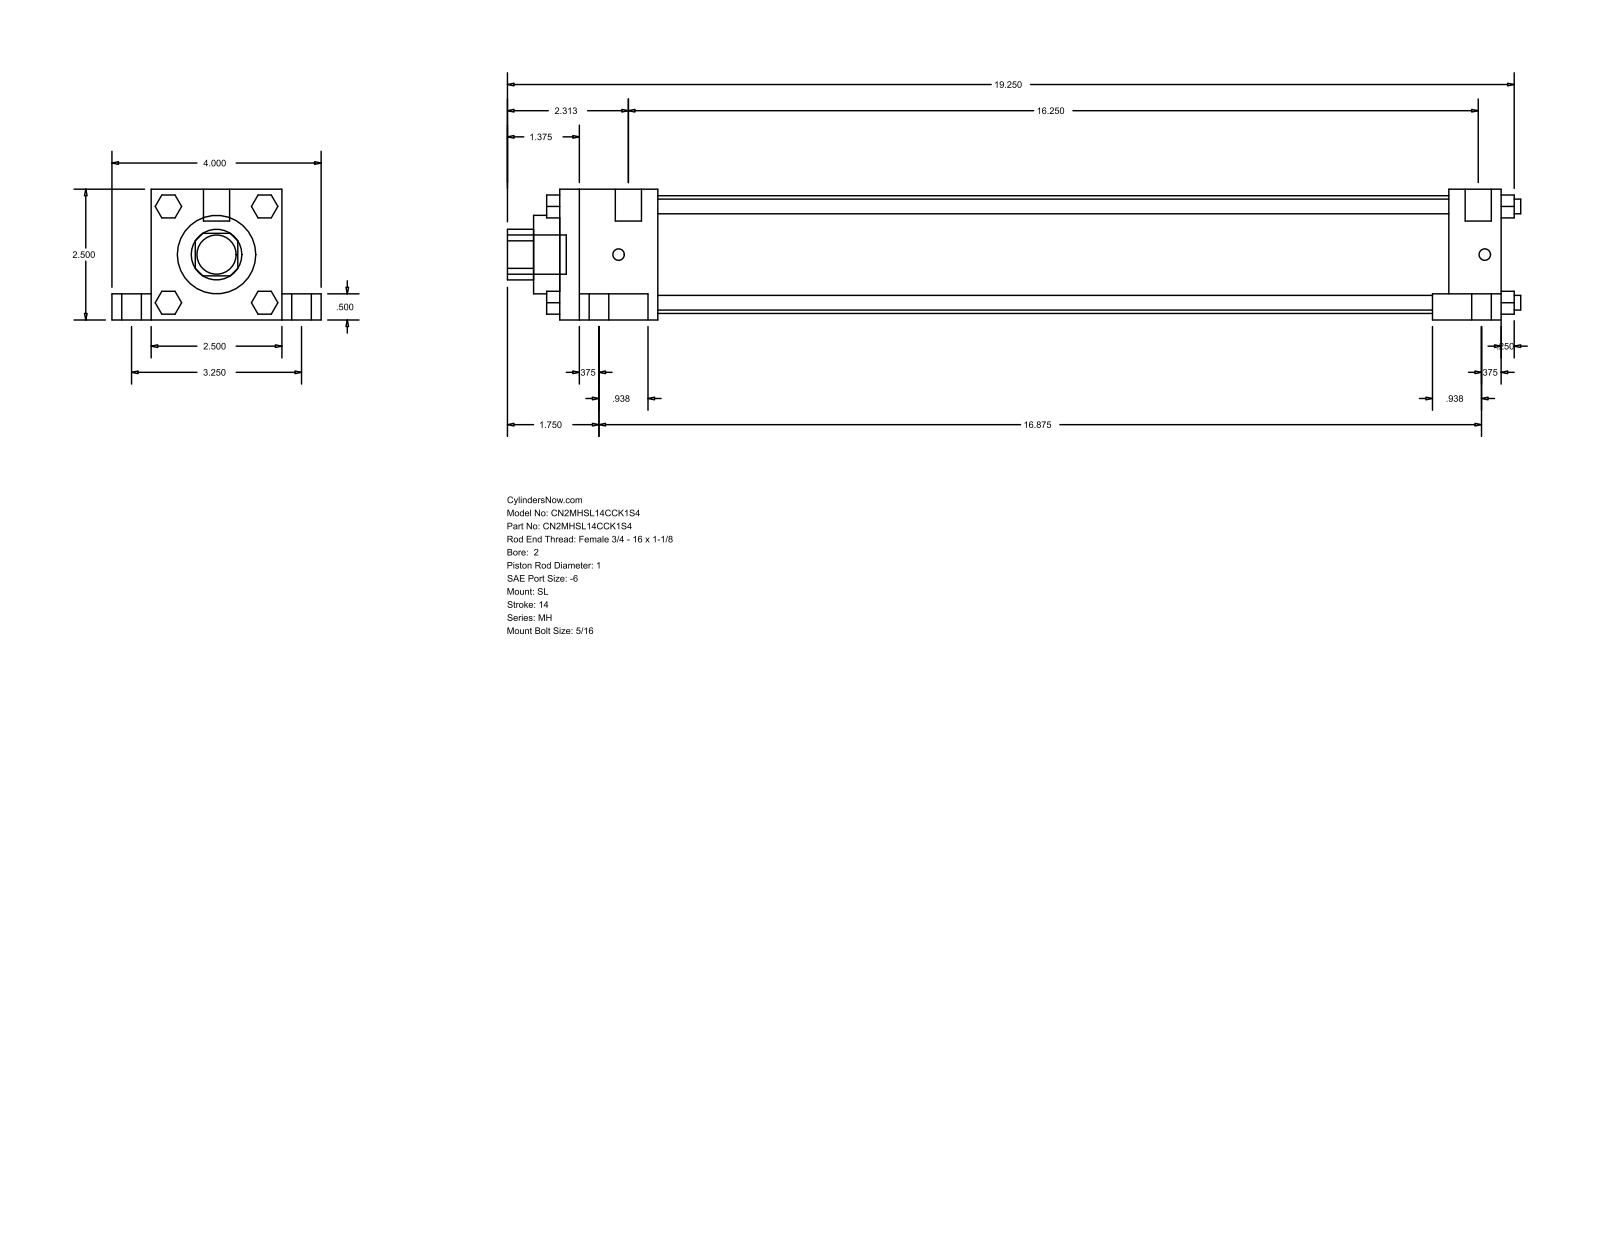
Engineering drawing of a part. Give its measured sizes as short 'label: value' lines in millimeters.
name: MH_SL__0200_1
written by: GSSL Pune (CONFIG_CONTROL_DESIGN)
unit: mm
bodies: 0 solids, 148 faces (112 planar, 36 cylindrical, 0 other)
size: 492.12 × 101.6 × 63.5
holes: 1× ⌀25.4, 1× ⌀38.1, 1× ⌀57.15
bosses: 4× ⌀15.88, 4× ⌀9.53, 4× ⌀7.14, 4× ⌀5.56, 2× ⌀12.7, 1× ⌀19.05
rounds: 1× R12.29
face distances: 63.5, 457.2, 12.7, 19.05, 50.8, 82.55, 9.52, 25.4, 431.8, 47.63
